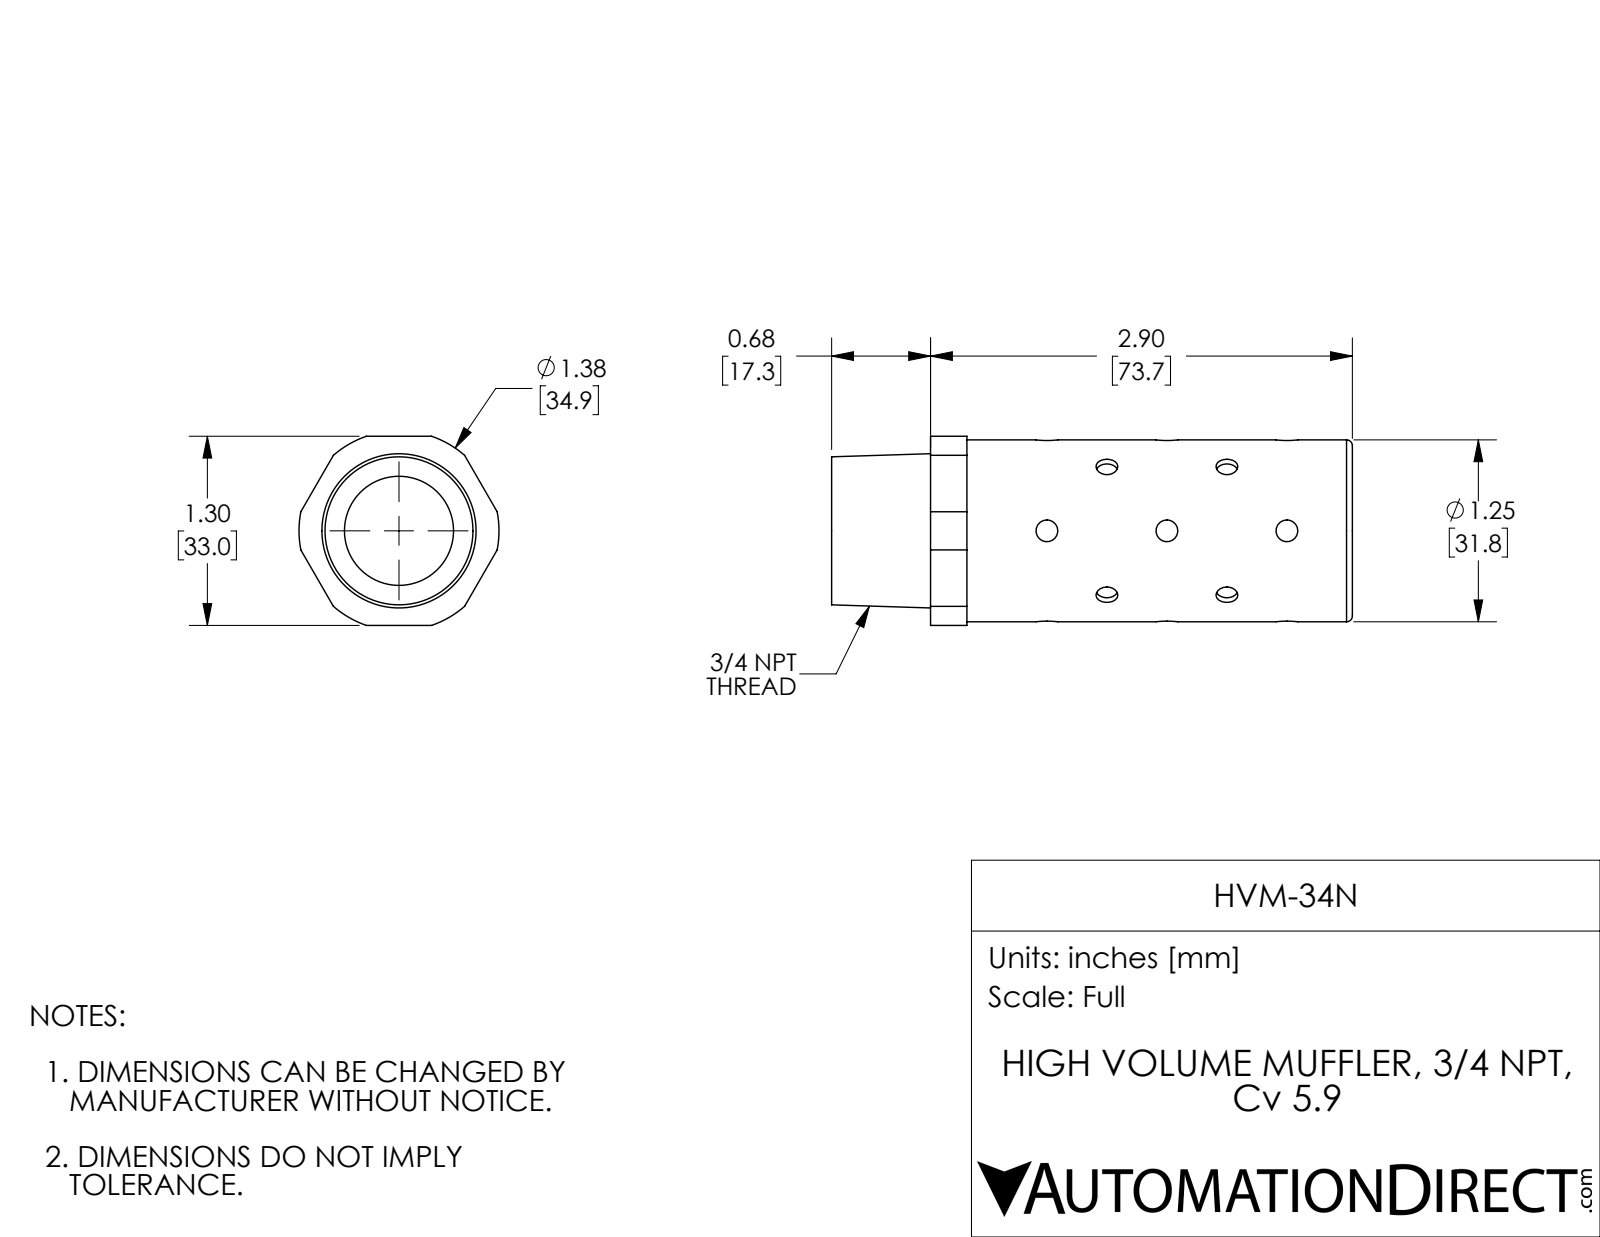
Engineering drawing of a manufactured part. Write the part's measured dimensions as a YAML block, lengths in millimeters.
part_name: "HVM-34N"
step_written_by: "SolidWorks 2017 (AUTOMOTIVE_DESIGN)"
units: millimeters
bodies: {solids: 1, faces: 86, planar: 31, cylindrical: 51, other: 4}
overall_size: [90.9, 34.9, 33]
volume: 44130
surface_area: 15930
round_holes:
  - {diameter: 3.8, count: 10}
  - {diameter: 19.1, count: 1}
round_bosses_or_shafts:
  - {diameter: 31.8, count: 1}
partial_cylinders:
  - {radius: 17.4, count: 1}
face_to_face_distances: [6.4, 67.3, 73.7, 17.3, 84.6, 90.9, 33, 23.6, 61, 1.9]
hole_center_spacings: [21, 21, 41.9]
